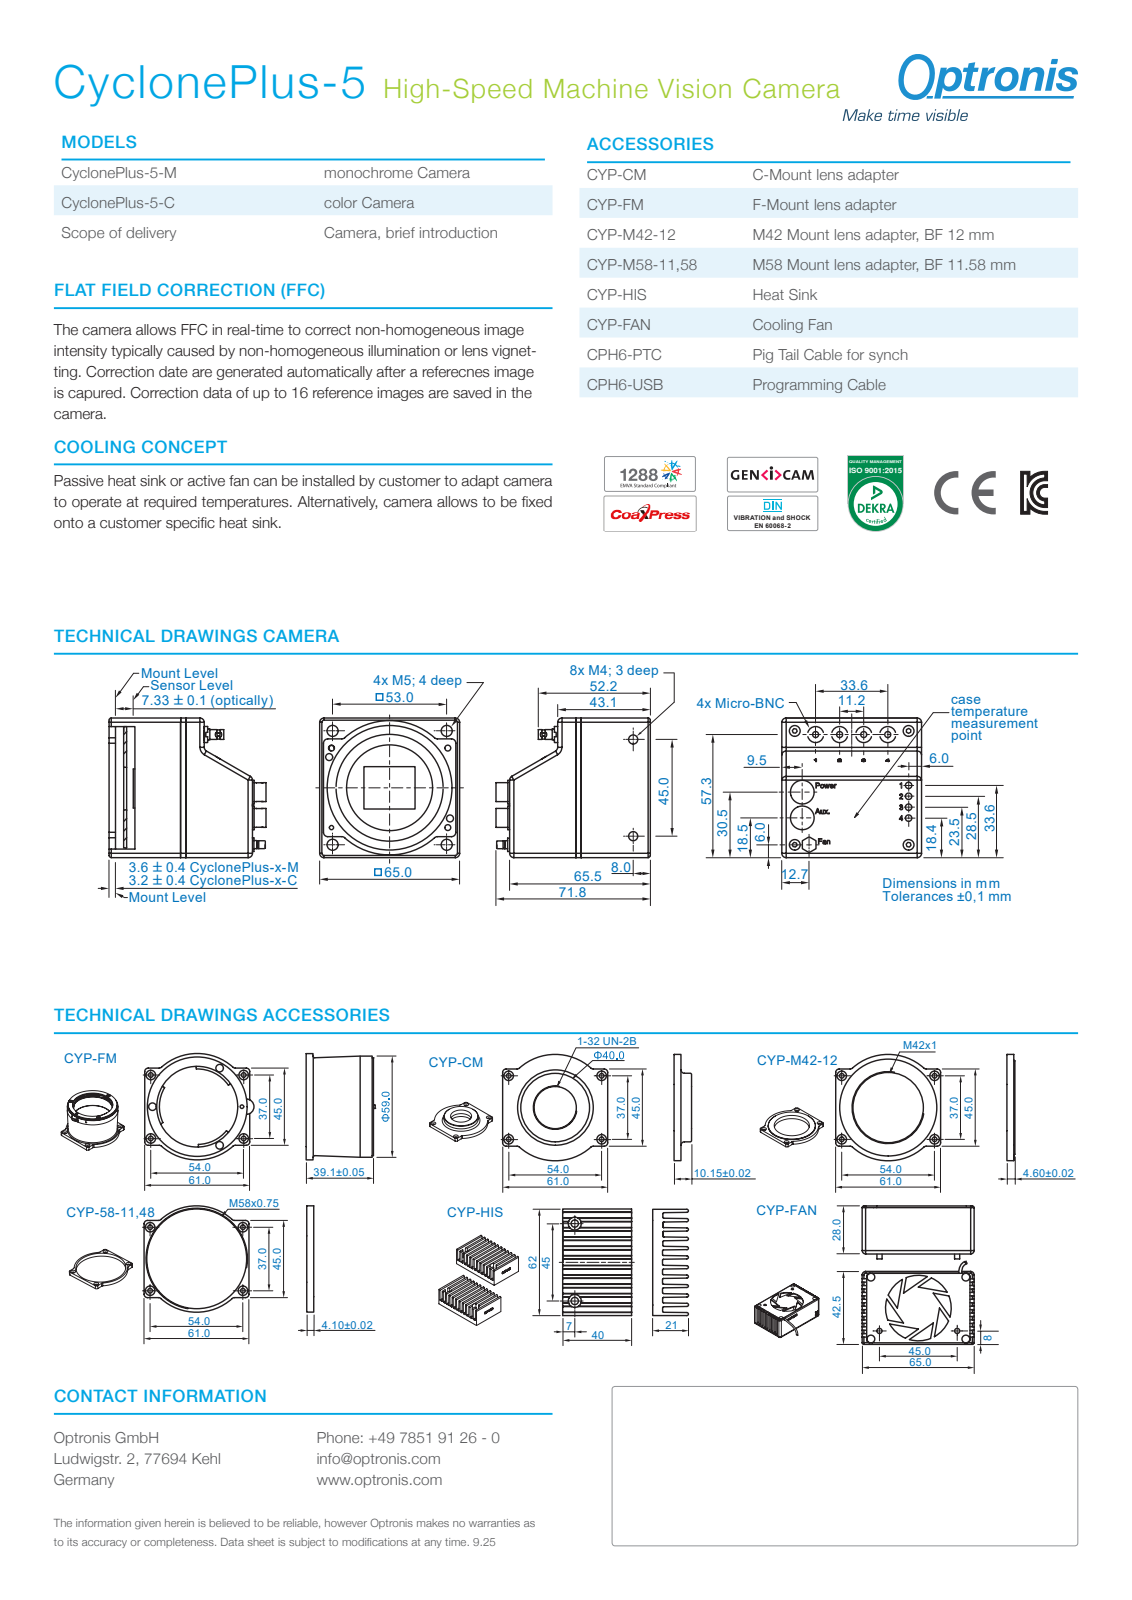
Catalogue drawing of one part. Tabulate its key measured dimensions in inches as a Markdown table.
| quantity | value |
| --- | --- |
| part name | 1200-MG-47_CycloneX_short |
| STEP written by | Autodesk Inventor 2026 (AUTOMOTIVE_DESIGN) |
| units | inches |
| bodies | 7 solids, 3808 faces (1927 planar, 1411 cylindrical, 470 other) |
| overall size | 2.827 × 2.559 × 2.559 |
| volume | 4.153 in³ |
| surface area | 95.95 in² |
| round holes (diameter × count) | 0.031 × 18, 0.02 × 10, 0.062 × 8, 0.106 × 8, 0.018 × 4, 0.018 × 4, 0.079 × 4, 0.087 × 4, 0.12 × 4, 0.128 × 4, 0.141 × 4, 0.165 × 4 |
| round bosses / shafts (diameter × count) | 0.034 × 209, 0.012 × 209, 0.043 × 10, 0.15 × 8, 0.295 × 4, 0.249 × 4, 0.205 × 4, 0.179 × 4 |
| partial cylindrical surfaces (radius × count) | 0.008 × 58, 0.079 × 34, 0.118 × 34, 0.007 × 24, 0.039 × 24, 0.006 × 16, 0.02 × 12, 0.018 × 10 |
| main face-to-face distances | 0.079, 2.48, 2.559, 2.402, 1.106, 0.118, 1.051, 0.933, 0.055, 0.988 |
| hole center spacings | 1.796, 1.772, 0.441, 0.882, 0.316, 0.339, 0.452, 0.739 |
